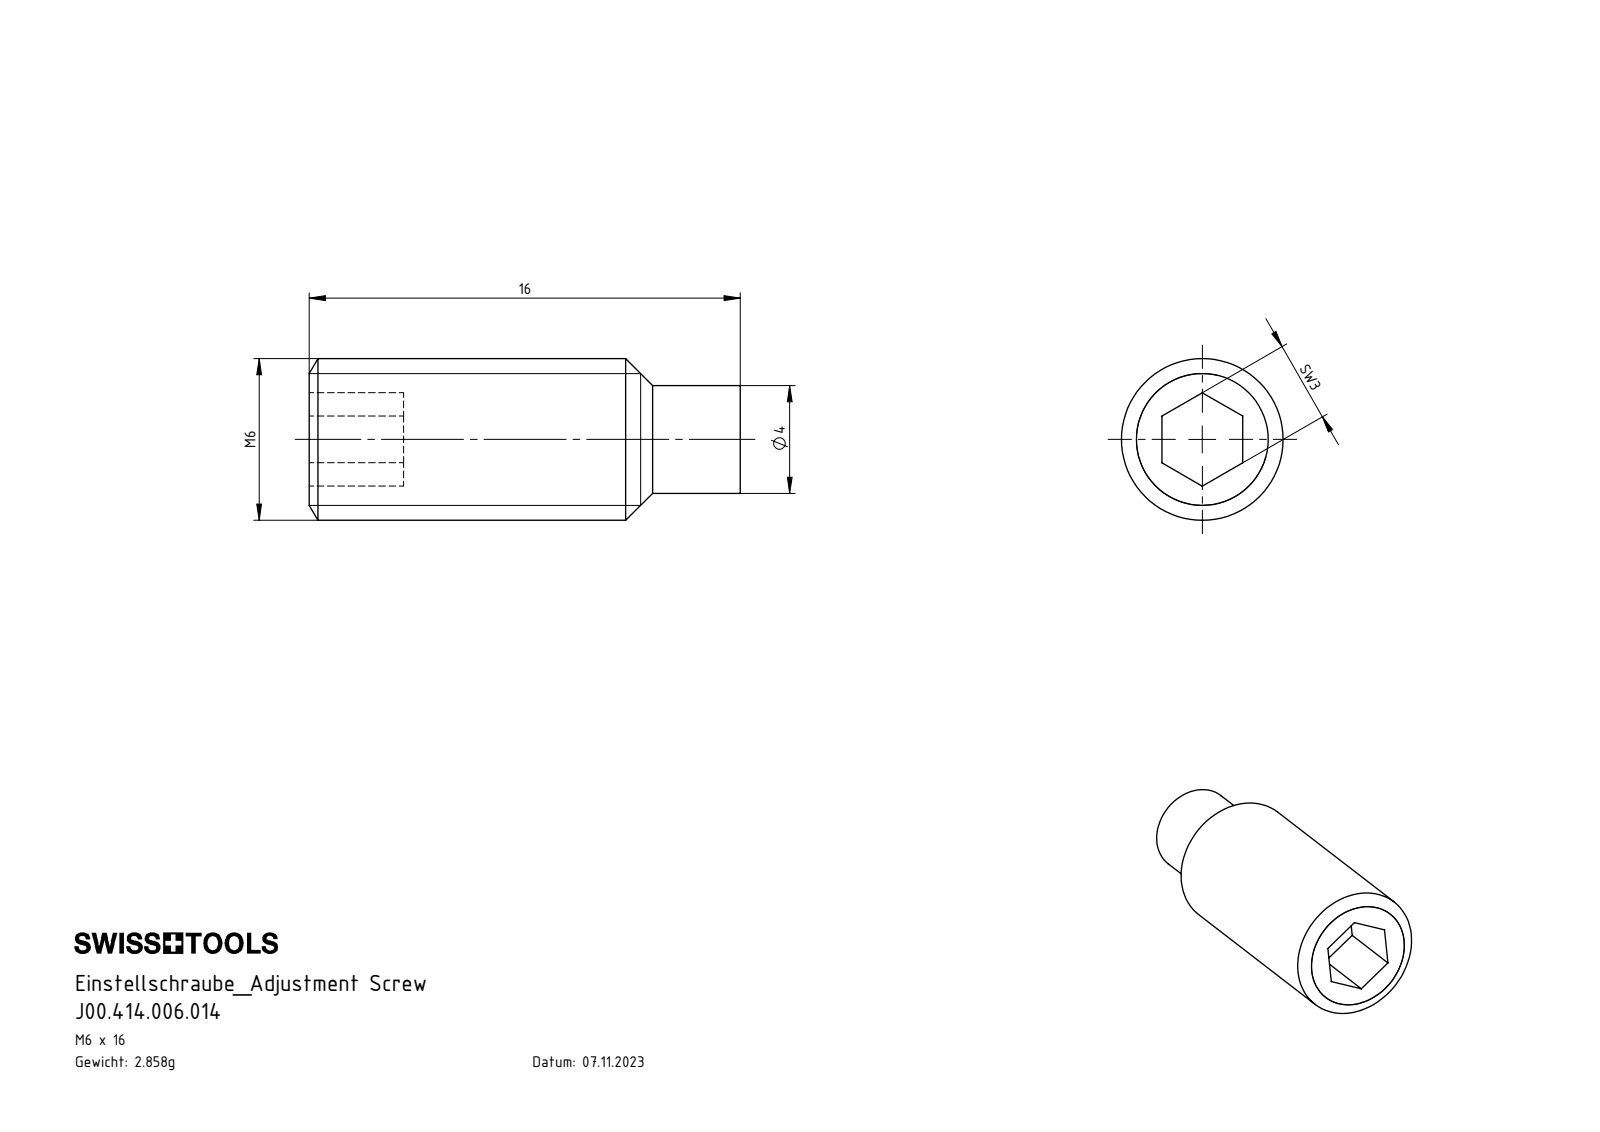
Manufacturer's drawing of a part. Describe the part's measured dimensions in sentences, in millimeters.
The part is named "J00.414.006.014". Its 3-D file was written by "SolidWorks 2022 (AUTOMOTIVE_DESIGN)". It is 1 solid with 17 faces: 9 planar, 4 cylindrical and 4 other. Overall it measures 16 by 6 by 6 millimeters. Its volume is 364 cubic millimeters and its surface area 357 square millimeters. Round bosses or shafts: 1 of diameter 6, 1 of diameter 4. The main face-to-face distances are 3, 16, 3.5, 12.5.
